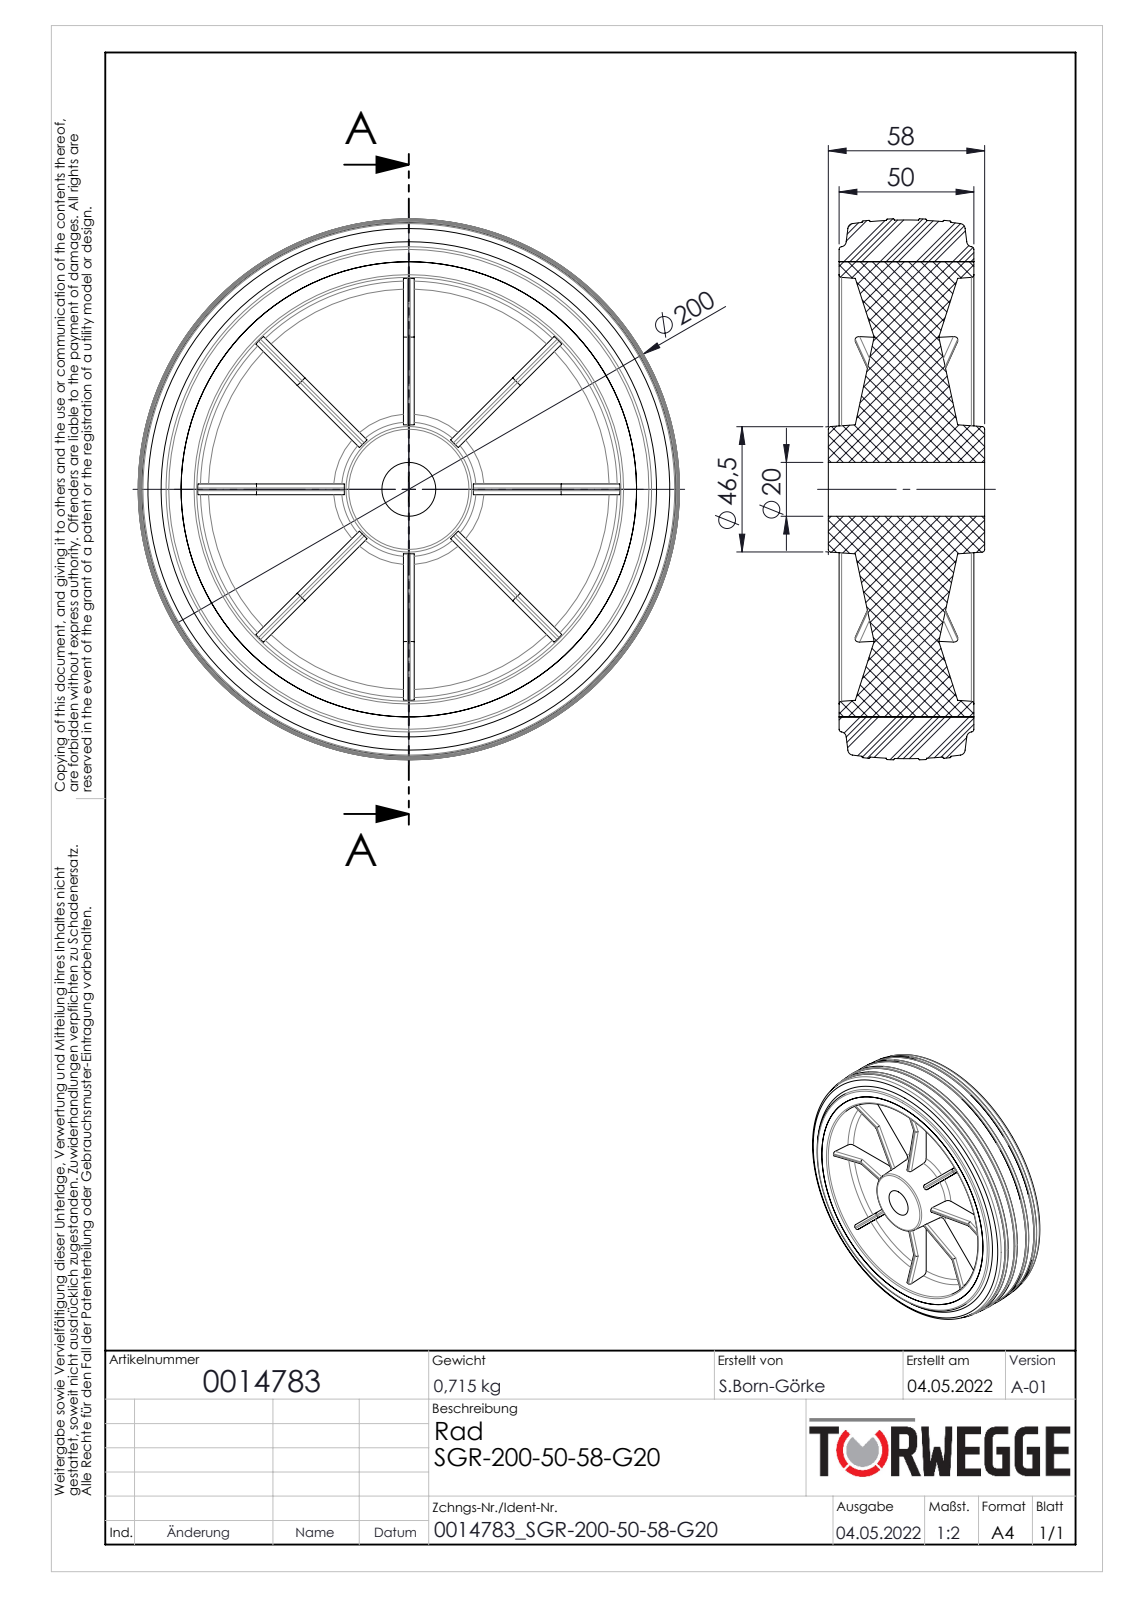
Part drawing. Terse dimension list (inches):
name: 0014783
written by: SolidWorks 2020 (AUTOMOTIVE_DESIGN)
unit: in
bodies: 2 solids, 270 faces (94 planar, 70 cylindrical, 106 other)
size: 7.907 × 7.907 × 2.283
volume: 47.25 in³; area: 299.8 in²
holes: 1× ⌀0.787, 1× ⌀6.654
rounds: 64× R0.059
face distances: 0.157, 1.063, 0.906, 1.969, 1.22, 2.126, 2.283, 0.354, 0.472, 0.492
